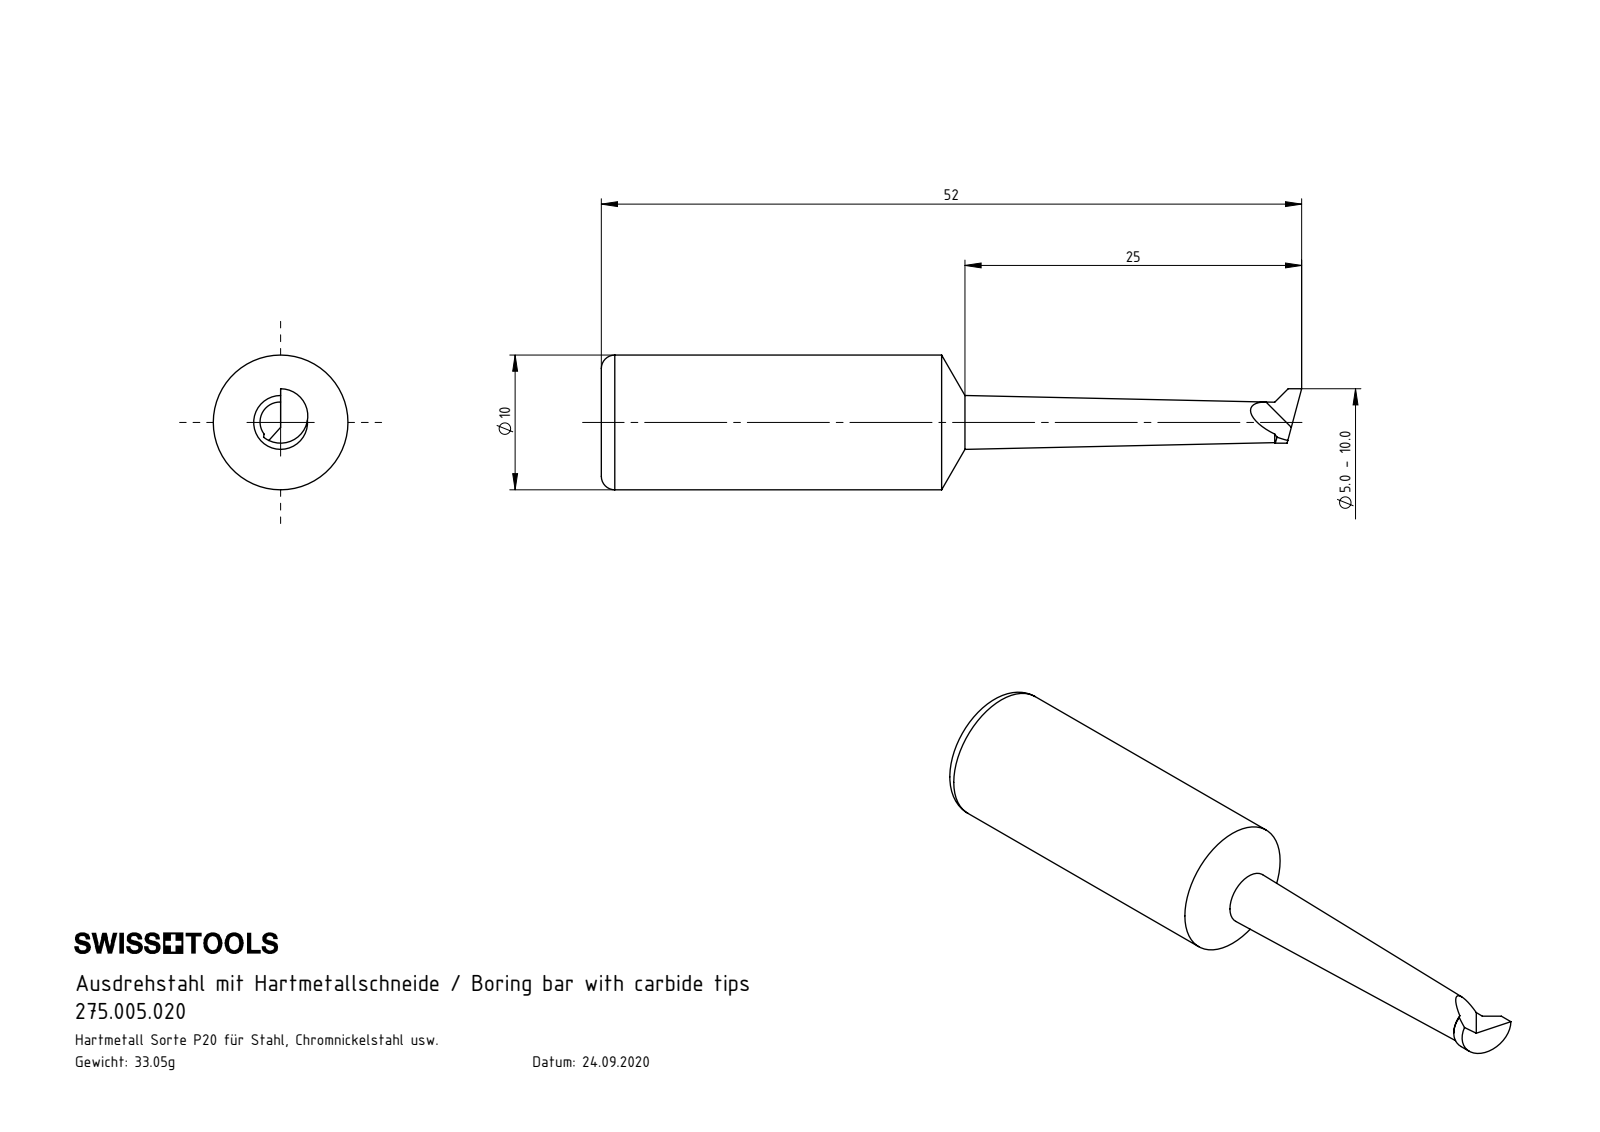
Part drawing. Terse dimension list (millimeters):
name: 275.005.020
written by: SolidWorks 2022 (AUTOMOTIVE_DESIGN)
unit: mm
bodies: 1 solid, 14 faces (4 planar, 3 cylindrical, 7 other)
size: 52 × 10 × 10
volume: 2 280 mm³; area: 1 212 mm²
bosses: 1× ⌀10
rounds: 1× R2.02
